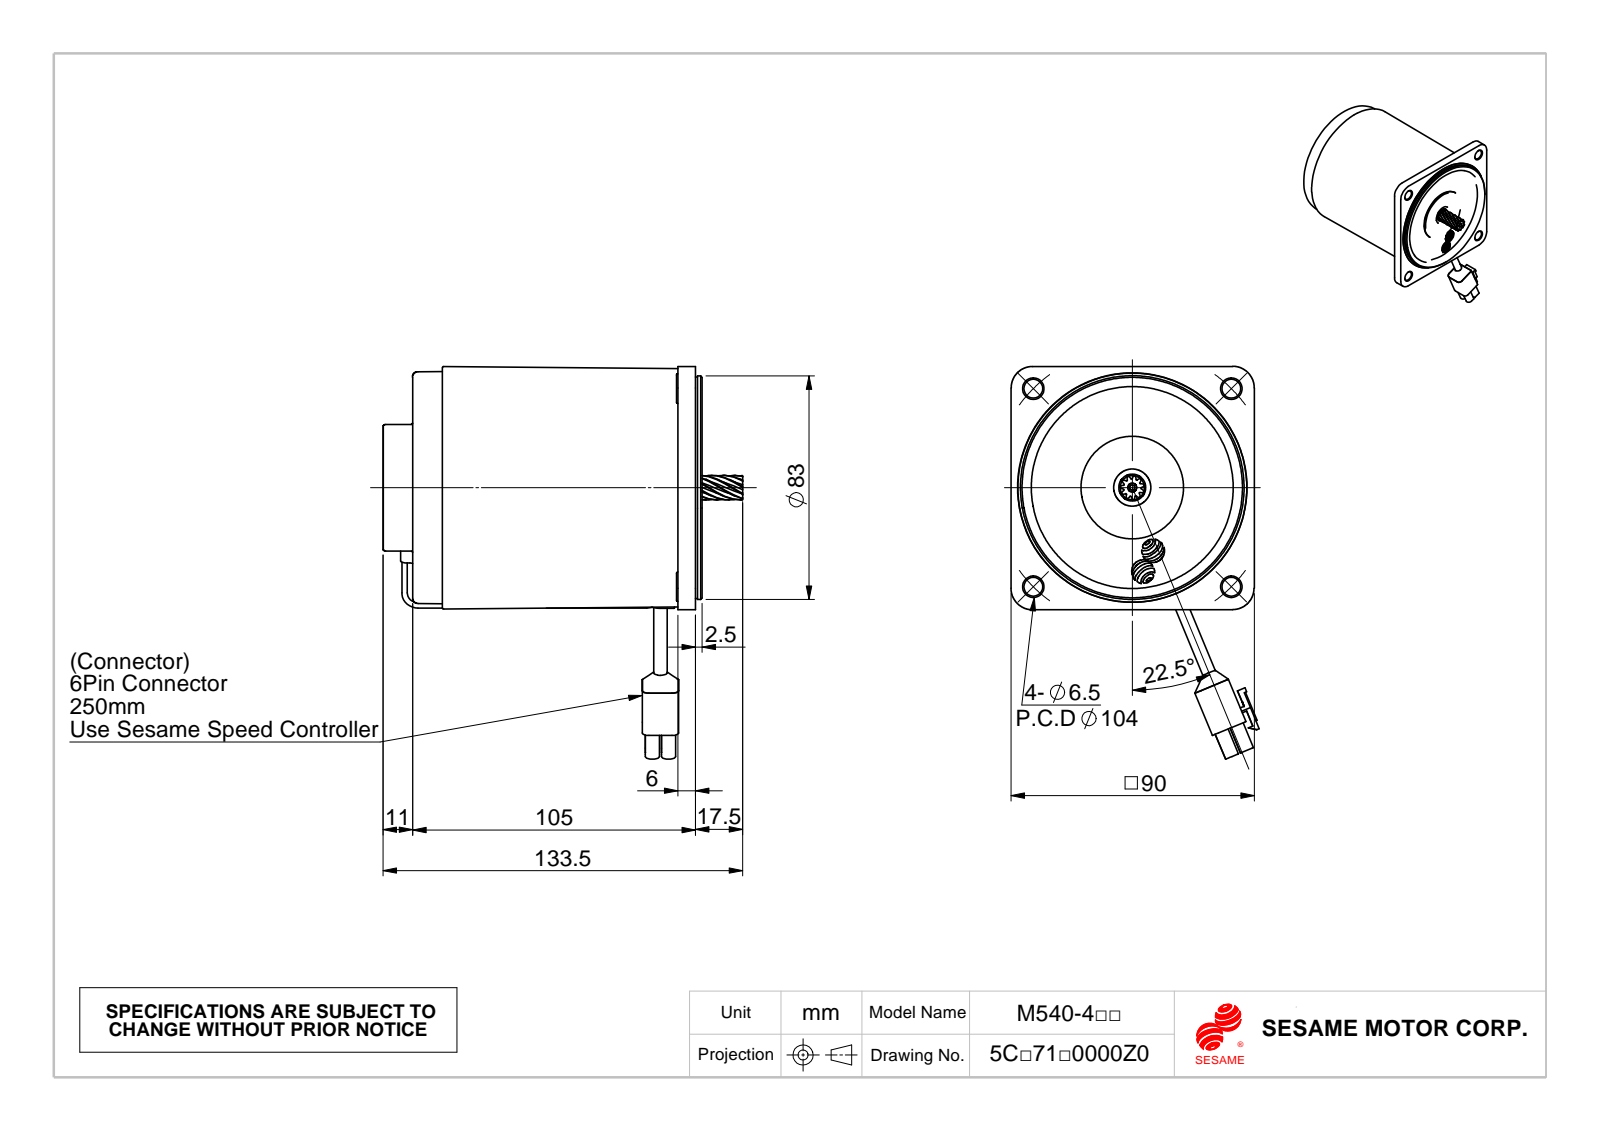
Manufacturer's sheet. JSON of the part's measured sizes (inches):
{"part_name": "公端子; M540-R; 60GN; 油封10x26x5 (+1 more)", "step_written_by": "SolidWorks 2010 (CONFIG_CONTROL_DESIGN)", "units": "inches", "bodies": {"solids": 8, "faces": 606, "planar": 166, "cylindrical": 296, "other": 144}, "overall_size": [5.739, 5.256, 3.625], "volume_in3": 44.13, "surface_area_in2": 123.1, "round_holes": [[0.15, 4], [0.217, 4], [0.276, 4], [0.098, 3], [0.079, 2], [0.122, 2], [0.283, 1], [0.374, 1], [0.539, 1], [0.827, 1], [0.945, 1], [1.024, 1]], "round_bosses_or_shafts": [[0.079, 2], [3.316, 1], [3.268, 1], [3.236, 1], [2.283, 1], [1.85, 1], [1.811, 1], [1.496, 1]], "partial_cylinders_radius": [[0.02, 14], [0.01, 8], [0.031, 8], [0.059, 8], [0.065, 8], [0.115, 8], [0.098, 7], [0.039, 6]], "face_to_face_distances": [4.031, 0.287, 3.744, 0.039, 4.075, 3.783, 4.071, 4.035, 0.291, 0.059], "hole_center_spacings": [0.236, 0.142, 0.167, 0.197, 1.503, 2.047, 2.881, 2.895]}
